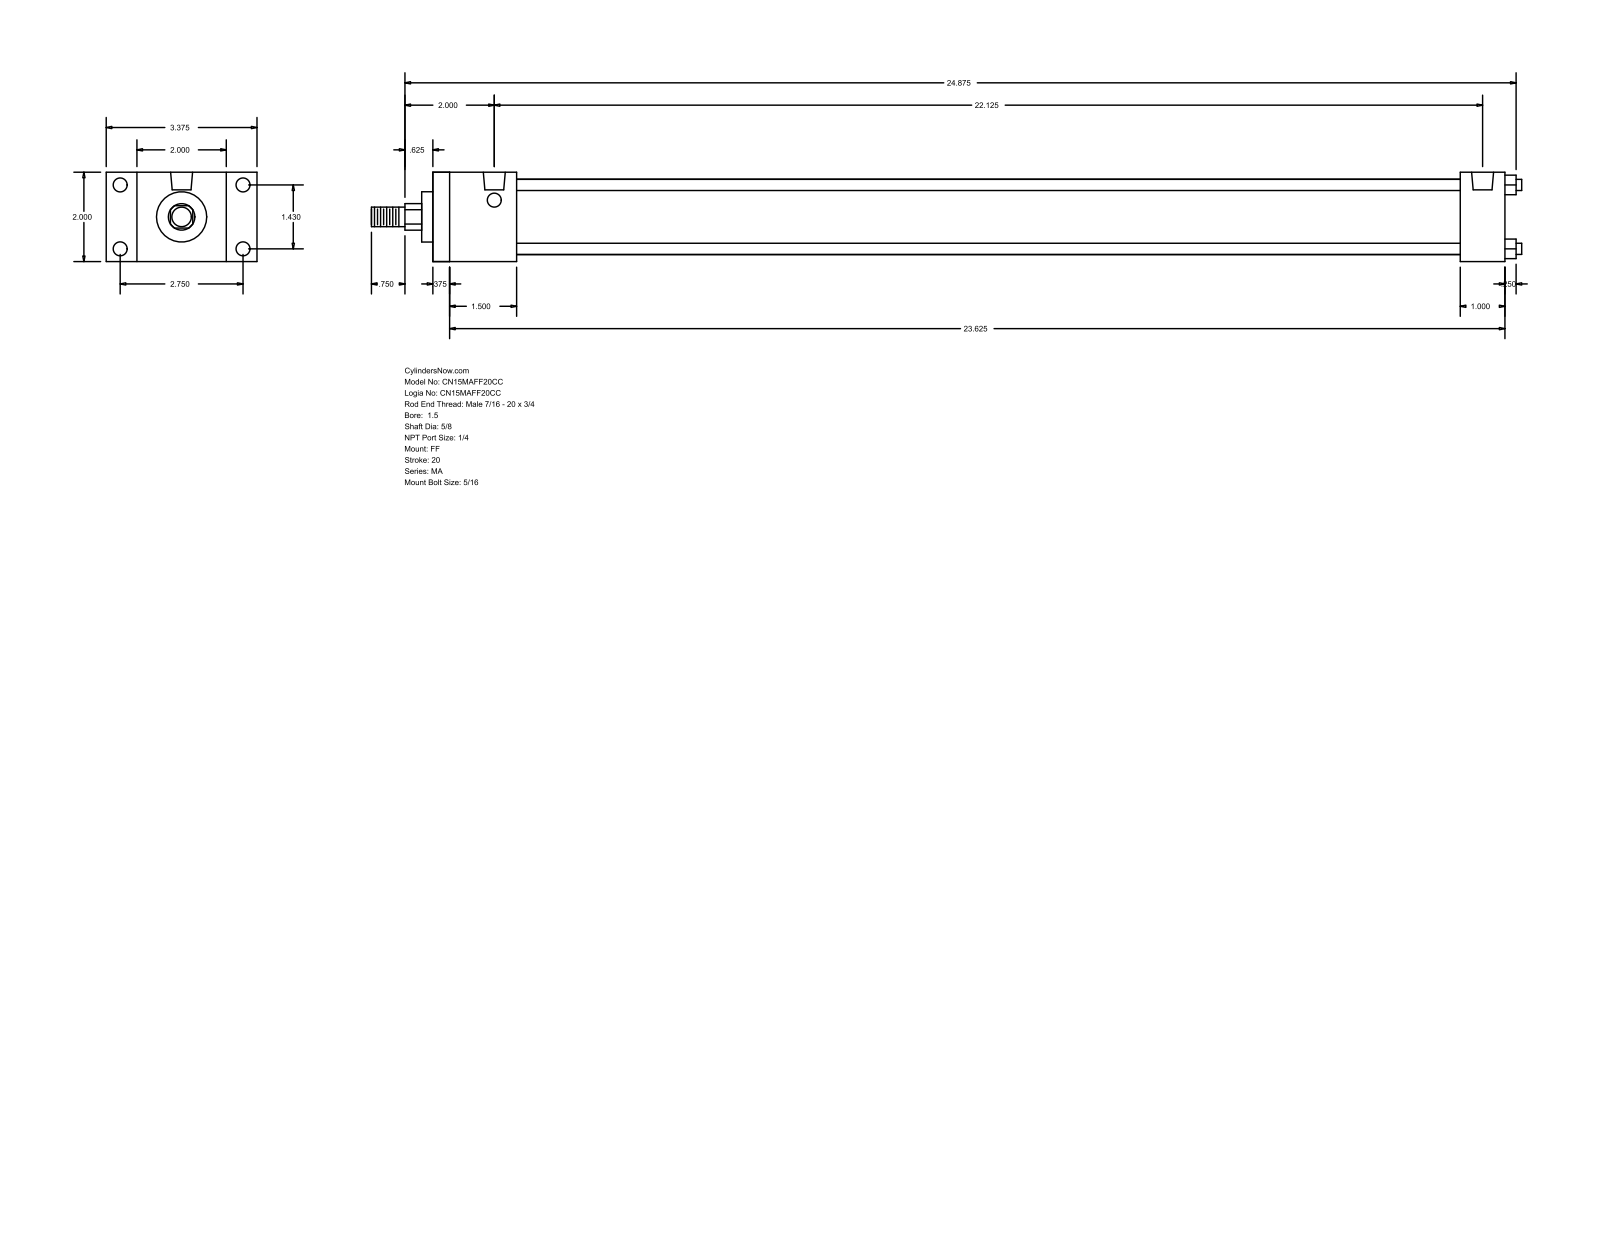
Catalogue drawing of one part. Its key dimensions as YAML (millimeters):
part_name: "MA_FF__0150_0.625"
step_written_by: "GSSL Pune (CONFIG_CONTROL_DESIGN)"
units: millimeters
bodies: {solids: 0, faces: 92, planar: 64, cylindrical: 28, other: 0}
overall_size: [654.05, 85.72, 50.8]
round_holes:
  - {diameter: 7.94, count: 8}
  - {diameter: 12.49, count: 2}
round_bosses_or_shafts:
  - {diameter: 6.35, count: 4}
  - {diameter: 42.93, count: 1}
  - {diameter: 28.57, count: 1}
  - {diameter: 15.88, count: 1}
  - {diameter: 11.11, count: 1}
partial_cylinders:
  - {radius: 7.54, count: 1}
face_to_face_distances: [50.8, 609.6, 9.52, 600.08, 25.4, 47.62, 584.2, 38.1, 574.68, 536.58]
hole_center_spacings: [36.32, 69.84, 78.72, 561.97]
